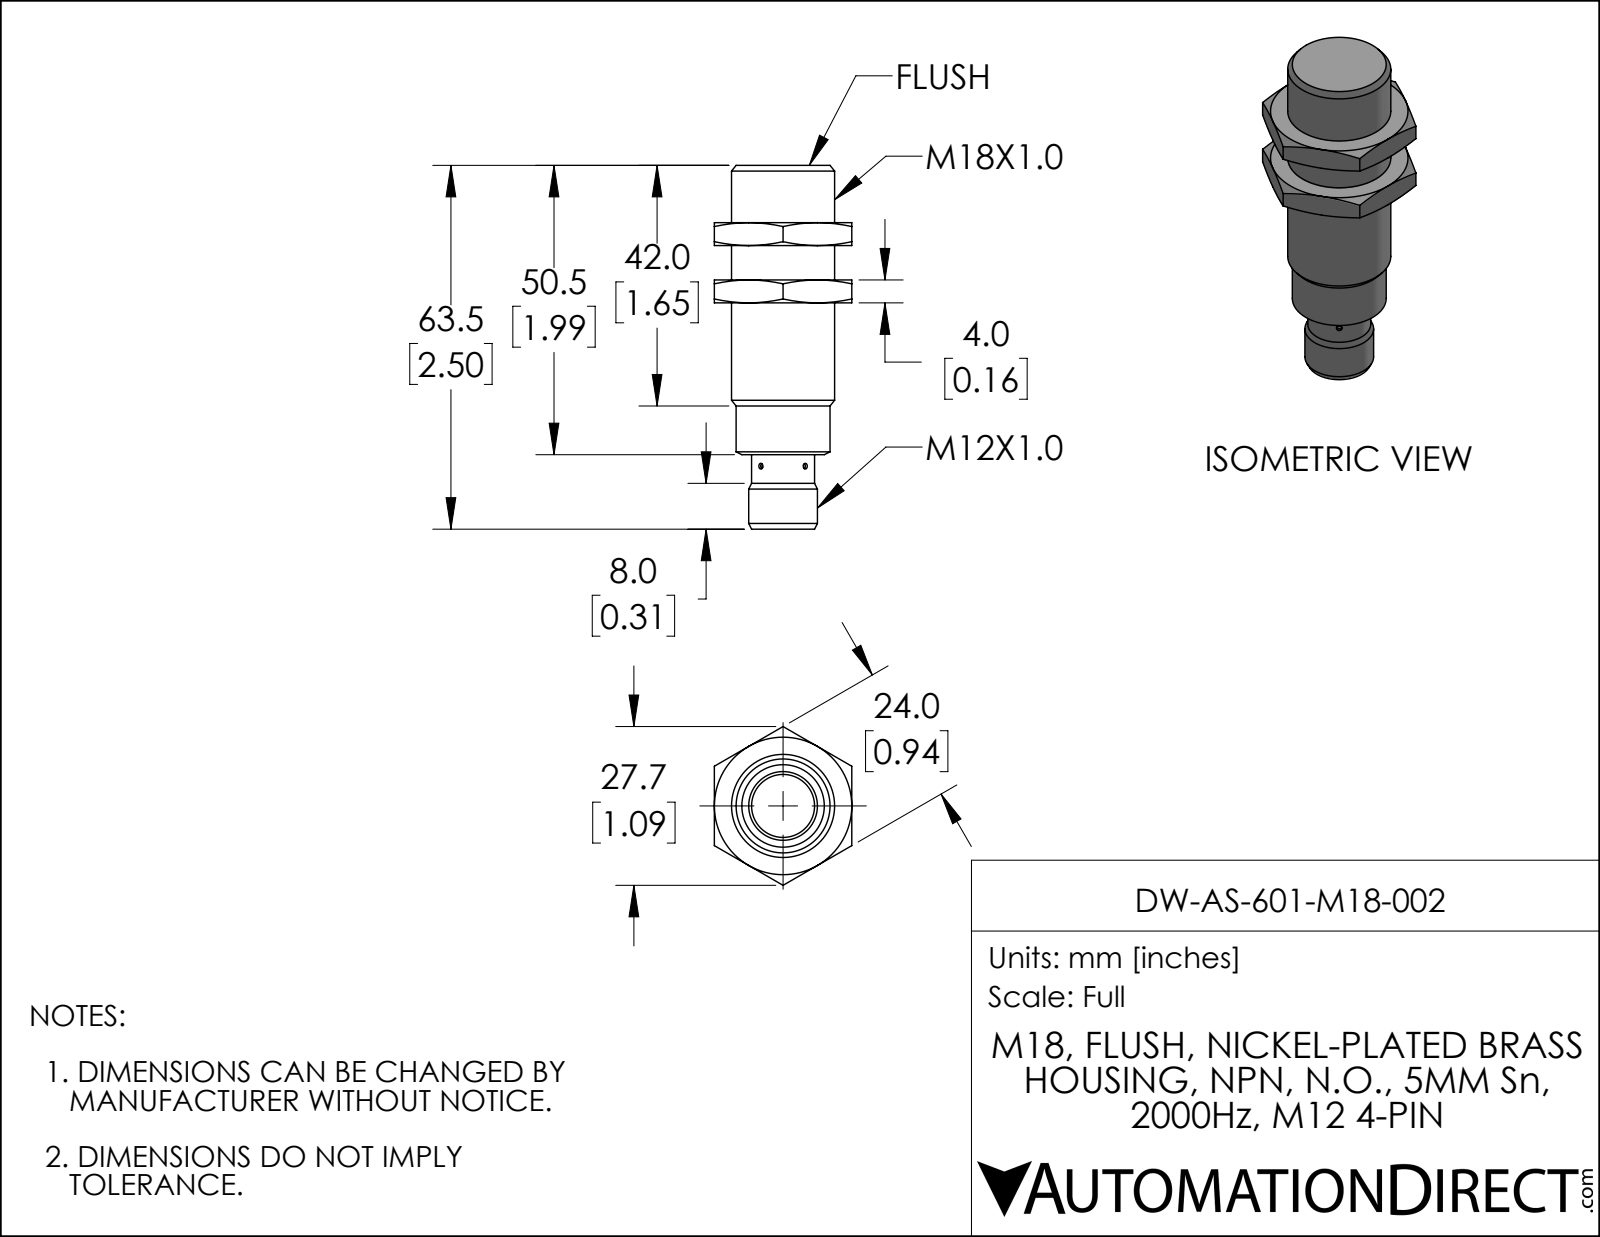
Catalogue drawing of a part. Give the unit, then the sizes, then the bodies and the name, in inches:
Units: inches
Overall size (bounding box): 2.5 × 1.091 × 0.945
Round holes (diameter × count): ⌀0.039 ×2
Round bosses / shafts (diameter × count): ⌀0.709 ×1, ⌀0.646 ×1, ⌀0.472 ×1, ⌀0.433 ×1
Main face-to-face distances: 0.394, 0.945, 0.551, 0.157, 0.787, 0.236, 2.5, 2.106, 1.949, 1.713
Volume: 0.958 in³ · Surface area: 7.52 in²
Bodies: 1 solid, 62 faces (23 planar, 10 cylindrical, 29 other)
Part name (STEP PRODUCT): DW-AS-601-M18-002
STEP written by: SolidWorks 2019 (AUTOMOTIVE_DESIGN)
